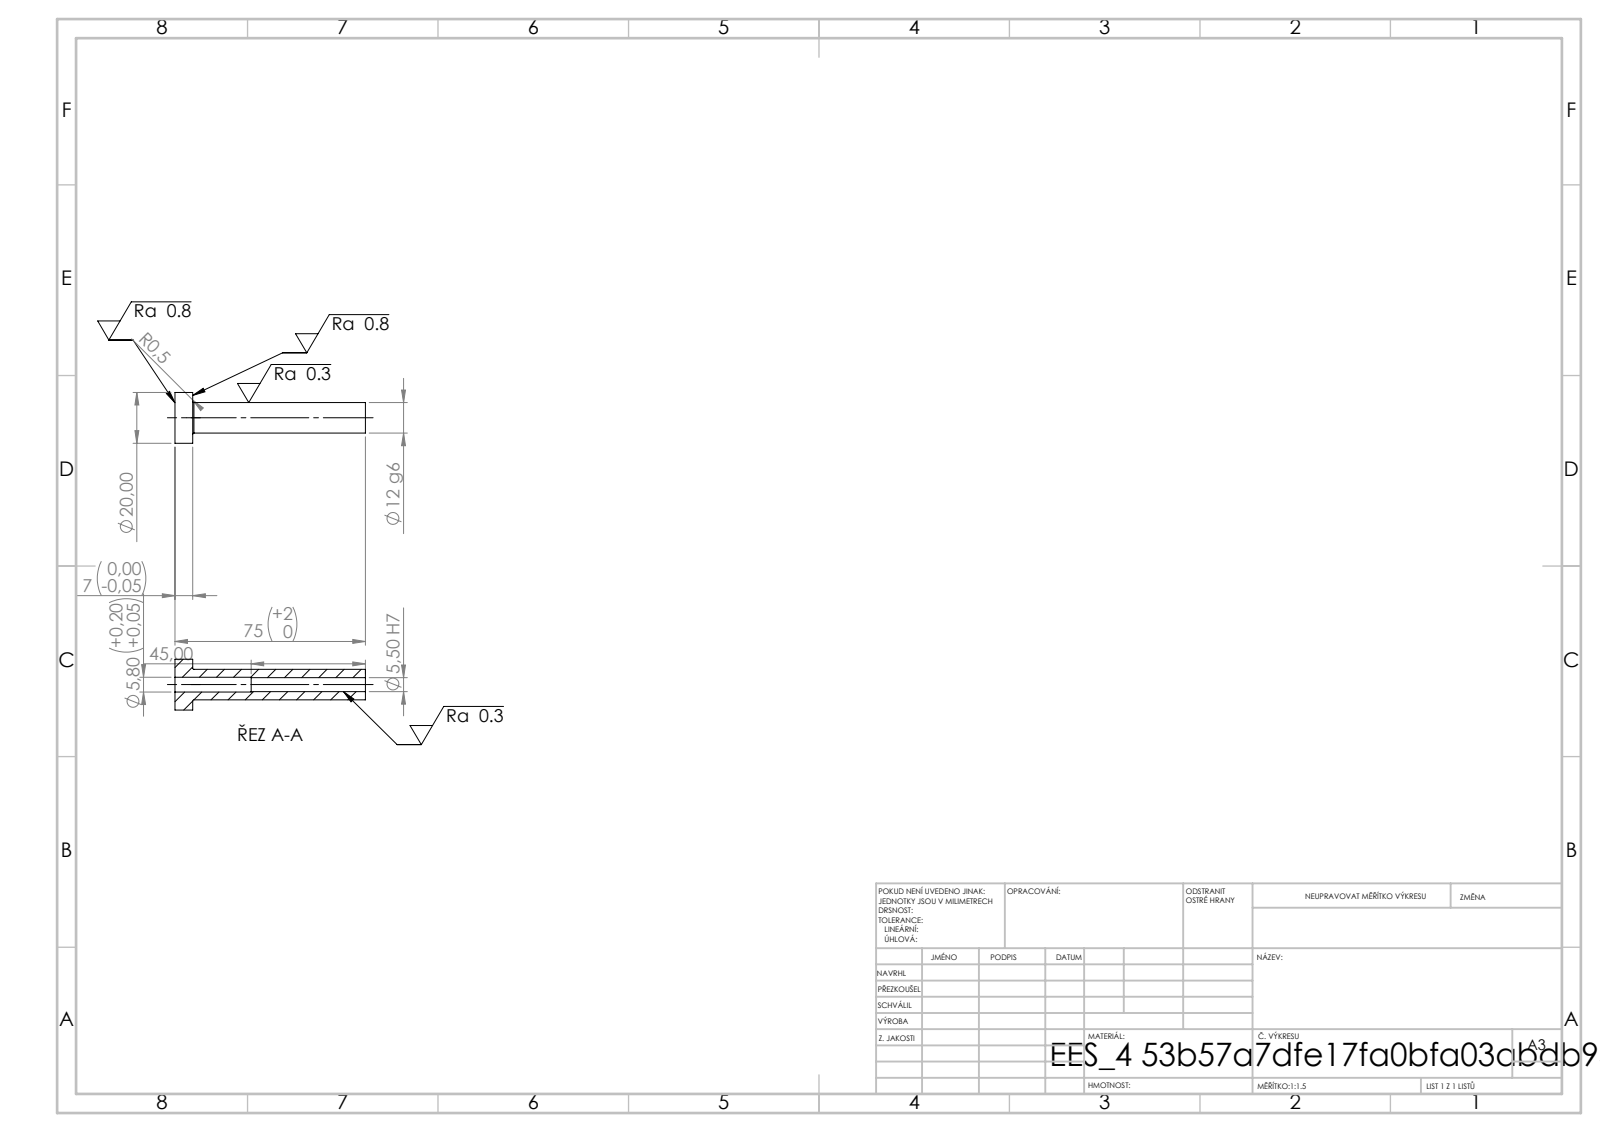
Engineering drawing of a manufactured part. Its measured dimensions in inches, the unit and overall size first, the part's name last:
Units: inches
Overall size (bounding box): 2.953 × 0.787 × 0.787
Round holes (diameter × count): ⌀0.217 ×1, ⌀0.228 ×1
Round bosses / shafts (diameter × count): ⌀0.787 ×1, ⌀0.472 ×1
Main face-to-face distances: 0.276, 2.953, 2.677, 1.181, 0.906, 1.772
Volume: 0.49 in³ · Surface area: 7.595 in²
Bodies: 1 solid, 14 faces (4 planar, 8 cylindrical, 2 other)
STEP written by: SolidWorks 2019 (CONFIG_CONTROL_DESIGN)
